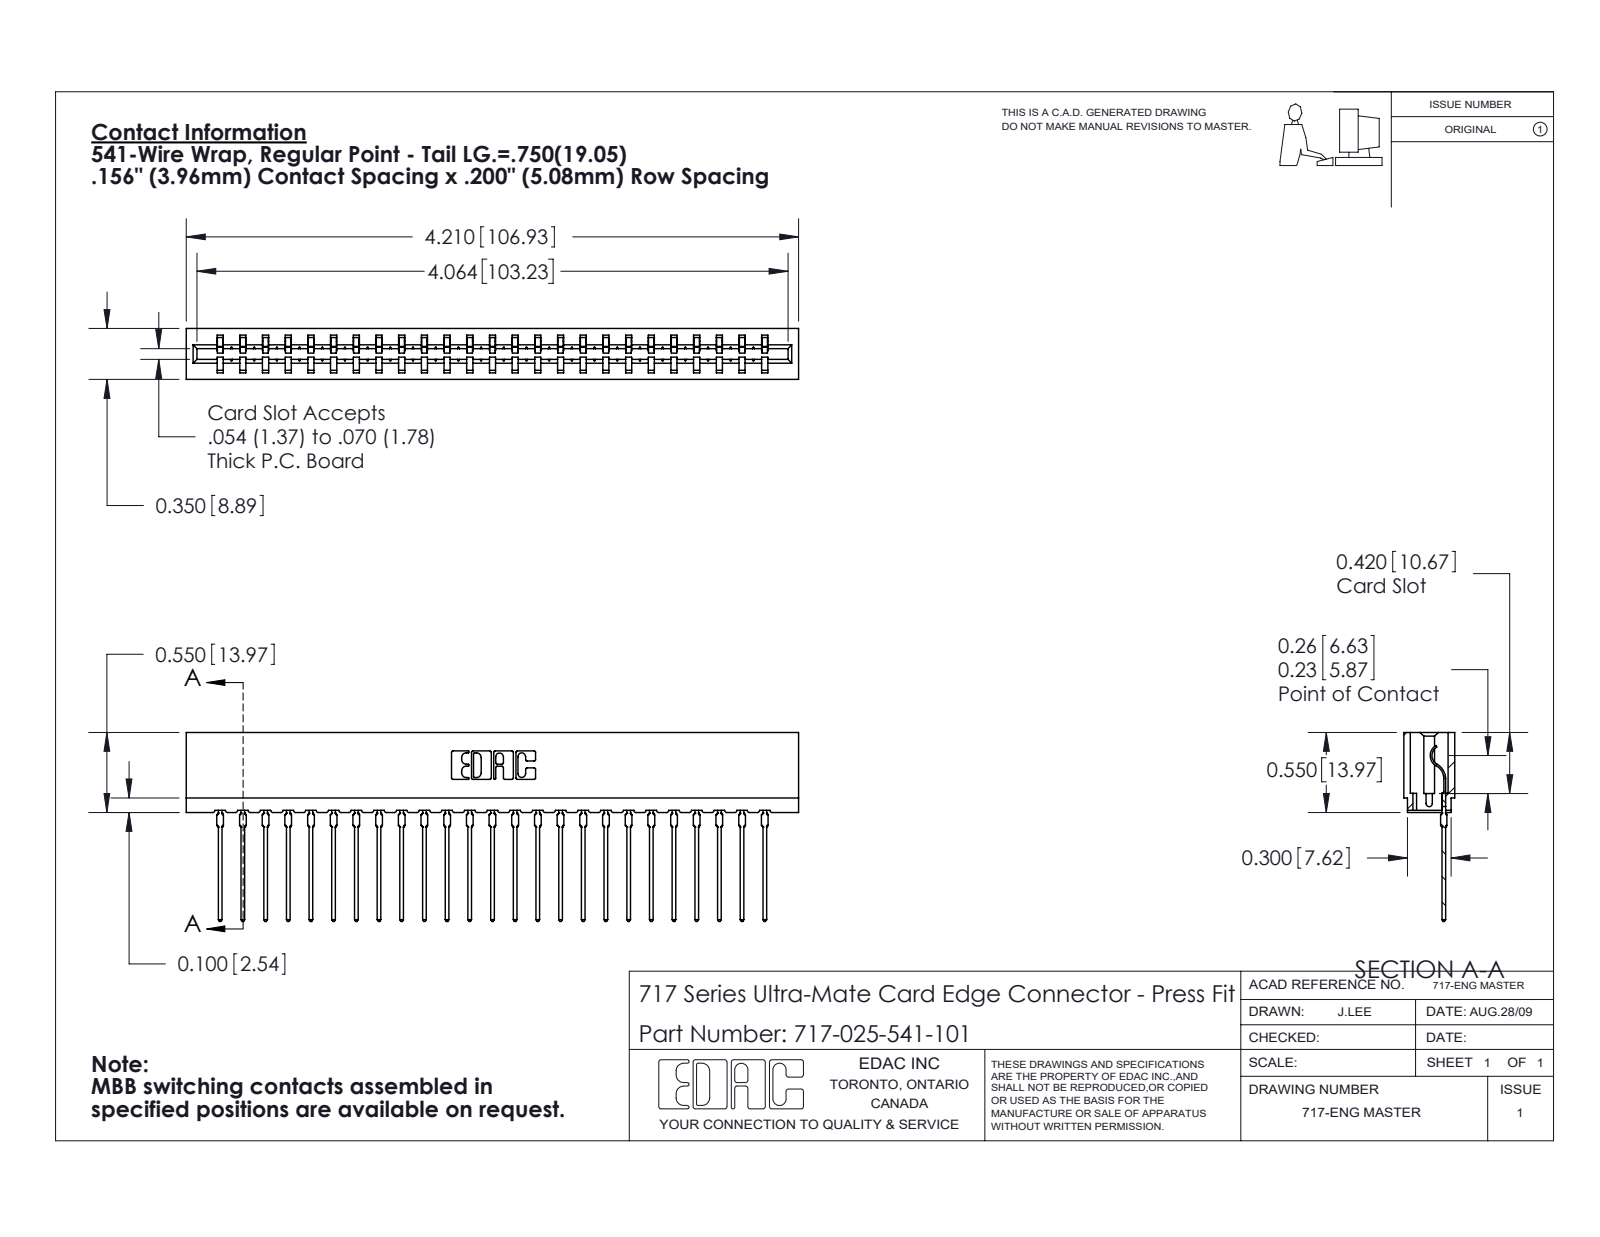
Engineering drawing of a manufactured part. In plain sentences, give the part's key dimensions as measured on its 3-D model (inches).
The part is named "717 Part_Insulator Option - 06; 717-025-541-101; 745-292-001_541". Its 3-D file was written by "SolidWorks 2020 (CONFIG_CONTROL_DESIGN)". It is 26 solids with 2919 faces: 1754 planar, 515 cylindrical and 650 other. Overall it measures 4.21 by 1.299 by 0.35 inches. Its volume is 0.562 cubic inches and its surface area 20.59 square inches. Partial cylindrical surfaces (rounded edges, fillets, slot ends): 50 of radius 0.015, 50 of radius 0.021, 22 of radius 0.01, 6 of radius 0.007, 6 of radius 0.031, 4 of radius 0.005, 4 of radius 0.011, 3 of radius 0.026. The main face-to-face distances are 0.212, 0.138, 0.35, 0.156, 0.063, 0.287, 0.076, 0.149, 0.074, 0.624.
